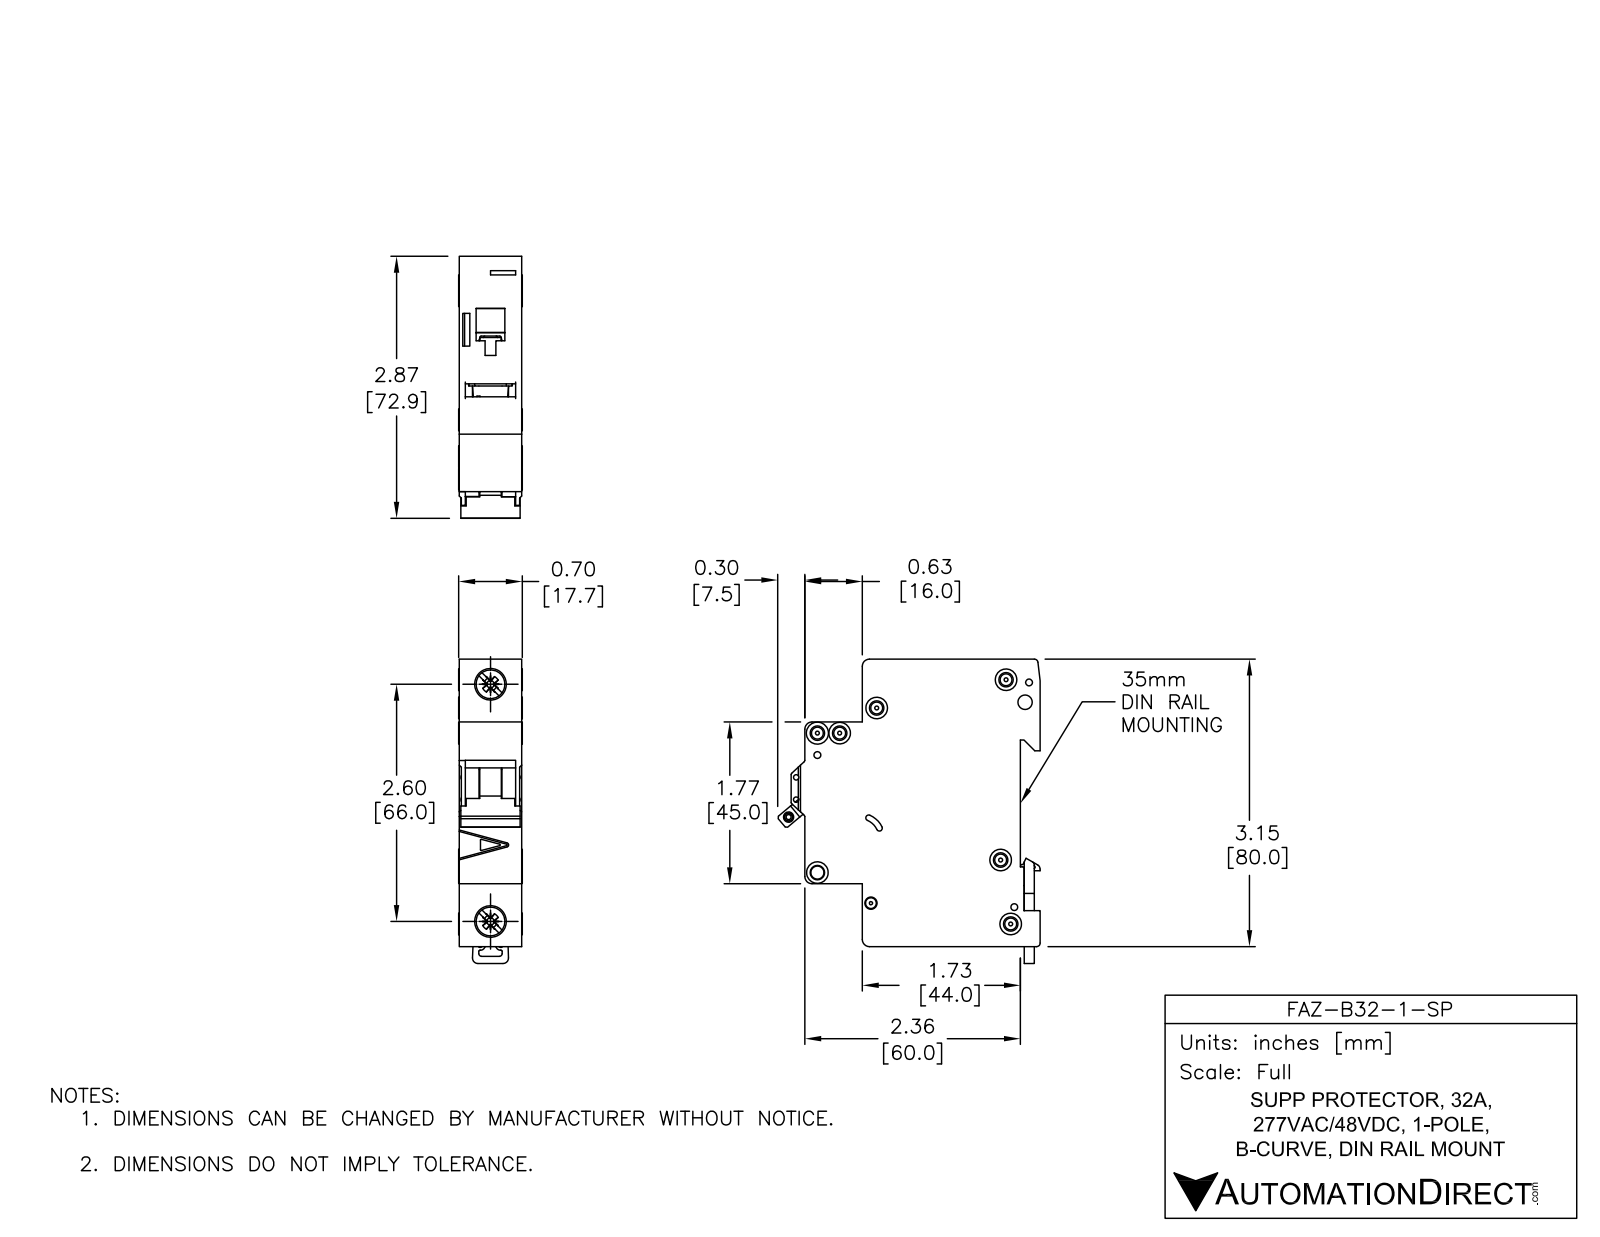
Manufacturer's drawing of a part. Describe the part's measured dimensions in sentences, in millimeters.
The part is named "FAZ-B32-1-SP". Its 3-D file was written by "SolidWorks 2014 (AUTOMOTIVE_DESIGN)". It is 5 solids with 558 faces: 235 planar, 202 cylindrical and 121 other. Overall it measures 84.78 by 73.04 by 17.7 millimeters. Its volume is 74 935 cubic millimeters and its surface area 19 545 square millimeters. Round holes: 6 of diameter 3.6, 3 of diameter 1.9, 2 of diameter 1.09, 2 of diameter 1.5, 2 of diameter 4, 2 of diameter 7.15, 1 of diameter 2.15, 1 of diameter 2.2, 1 of diameter 2.55, 1 of diameter 3.3, 1 of diameter 3.4. Round bosses or shafts: 4 of diameter 6, 2 of diameter 8.2, 1 of diameter 2.5. Partial cylindrical surfaces (rounded edges, fillets, slot ends): 30 of radius 0.25, 13 of radius 0.5, 8 of radius 2, 5 of radius 0.2, 4 of radius 1, 2 of radius 0.8, 2 of radius 3, 1 of radius 1.5. The main face-to-face distances are 17.5, 79.48, 5.5, 49.5, 44, 65.5, 60, 16, 1.75, 15.75. The hole center spacings are 6.2, 13.64, 4.81, 5.19, 5.61, 6.1, 6.44, 8.19.
